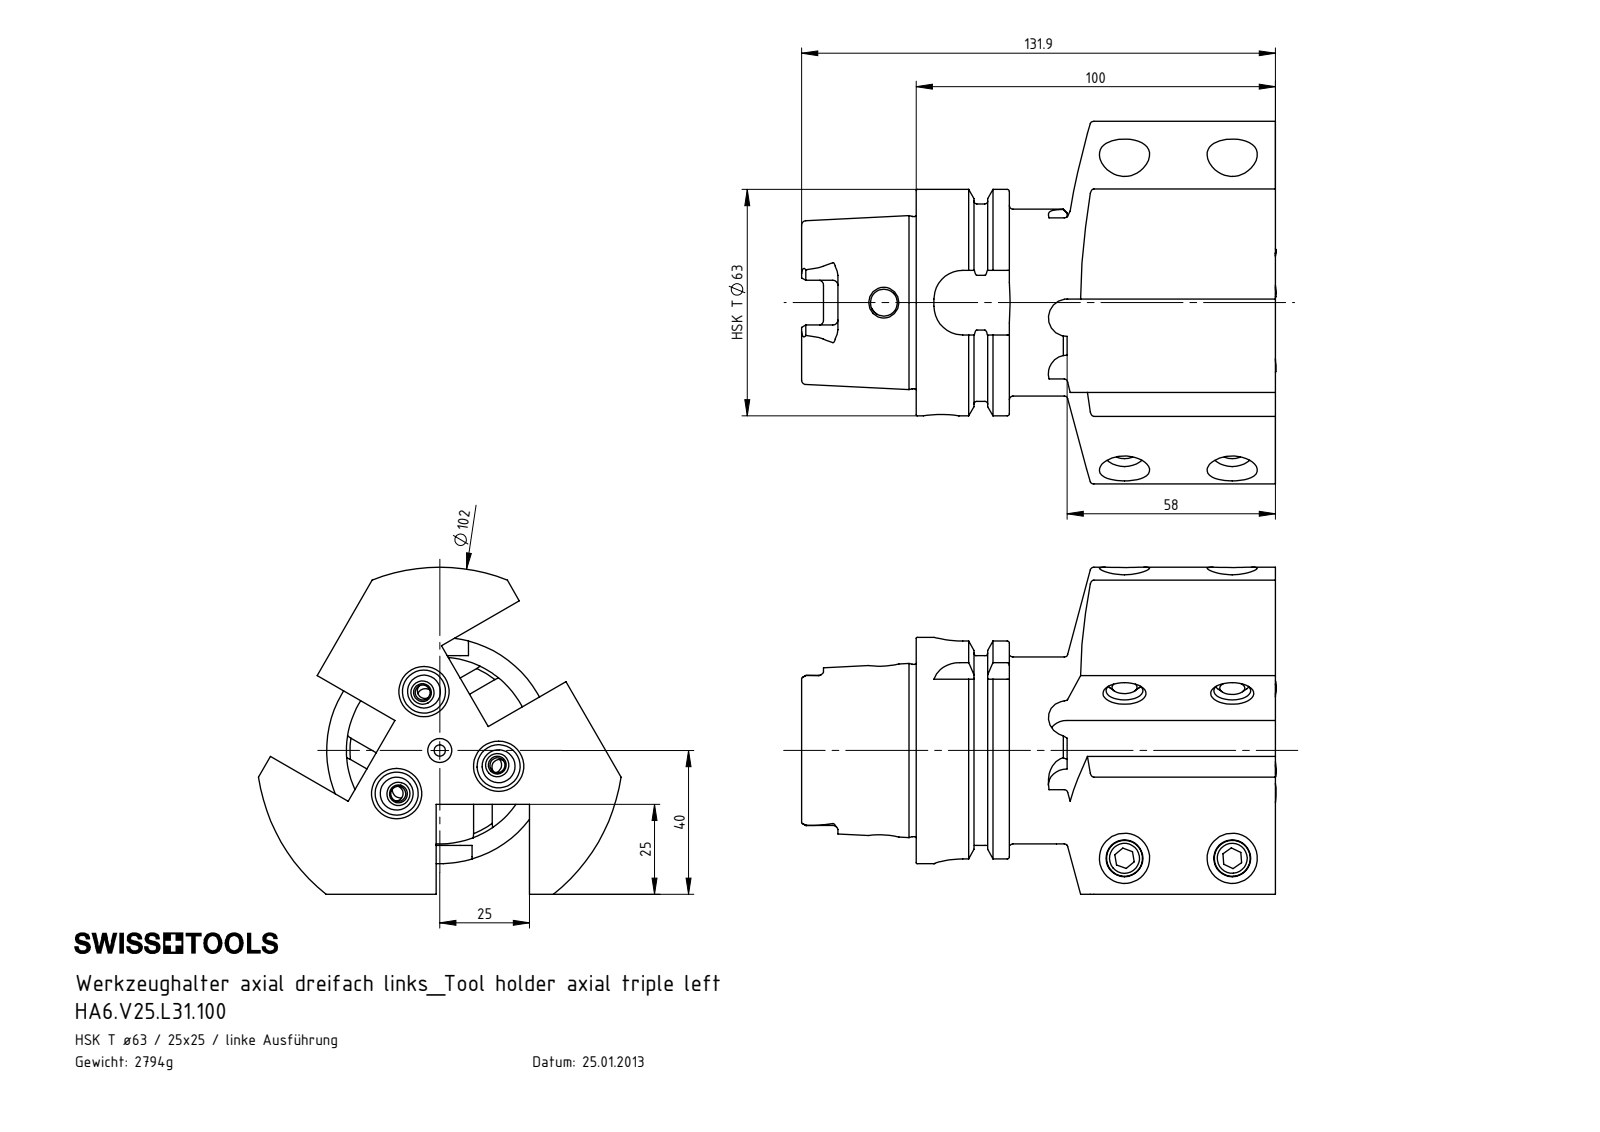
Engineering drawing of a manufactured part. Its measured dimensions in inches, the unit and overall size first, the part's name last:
Units: inches
Overall size (bounding box): 5.287 × 3.973 × 3.583
Round holes (diameter × count): ⌀0.551 ×9, ⌀0.197 ×6, ⌀0.404 ×6, ⌀0.394 ×4, ⌀0.124 ×1, ⌀0.295 ×1, ⌀0.331 ×1, ⌀0.669 ×1, ⌀0.748 ×1, ⌀1.339 ×1, ⌀1.575 ×1
Round bosses / shafts (diameter × count): ⌀0.472 ×6, ⌀2.48 ×1, ⌀2.163 ×1, ⌀2.047 ×1, ⌀1.887 ×1
Partial cylindrical surfaces — rounded edges, fillets, slot ends (radius × count): R0.055 ×6, R0.205 ×6, R0.113 ×4, R0.315 ×4, R2.008 ×1
Main face-to-face distances: 0.984, 1.024, 3.937, 0.394, 3.543, 0.63, 1.022, 2.522, 2.915, 3.152
Hole centre spacings: 0.668, 1.157, 1.181, 2.281, 3.368
Volume: 22.13 in³ · Surface area: 122.8 in²
Bodies: 13 solids, 398 faces (127 planar, 122 cylindrical, 149 other)
Part name (STEP PRODUCT): ISO 4026 - M12 x 25; KU1-U14.001.012_1; HA6-V25.L31.100; KU1-U14.001.012_2 (+2 more)
STEP written by: SolidWorks 2015 (CONFIG_CONTROL_DESIGN)
